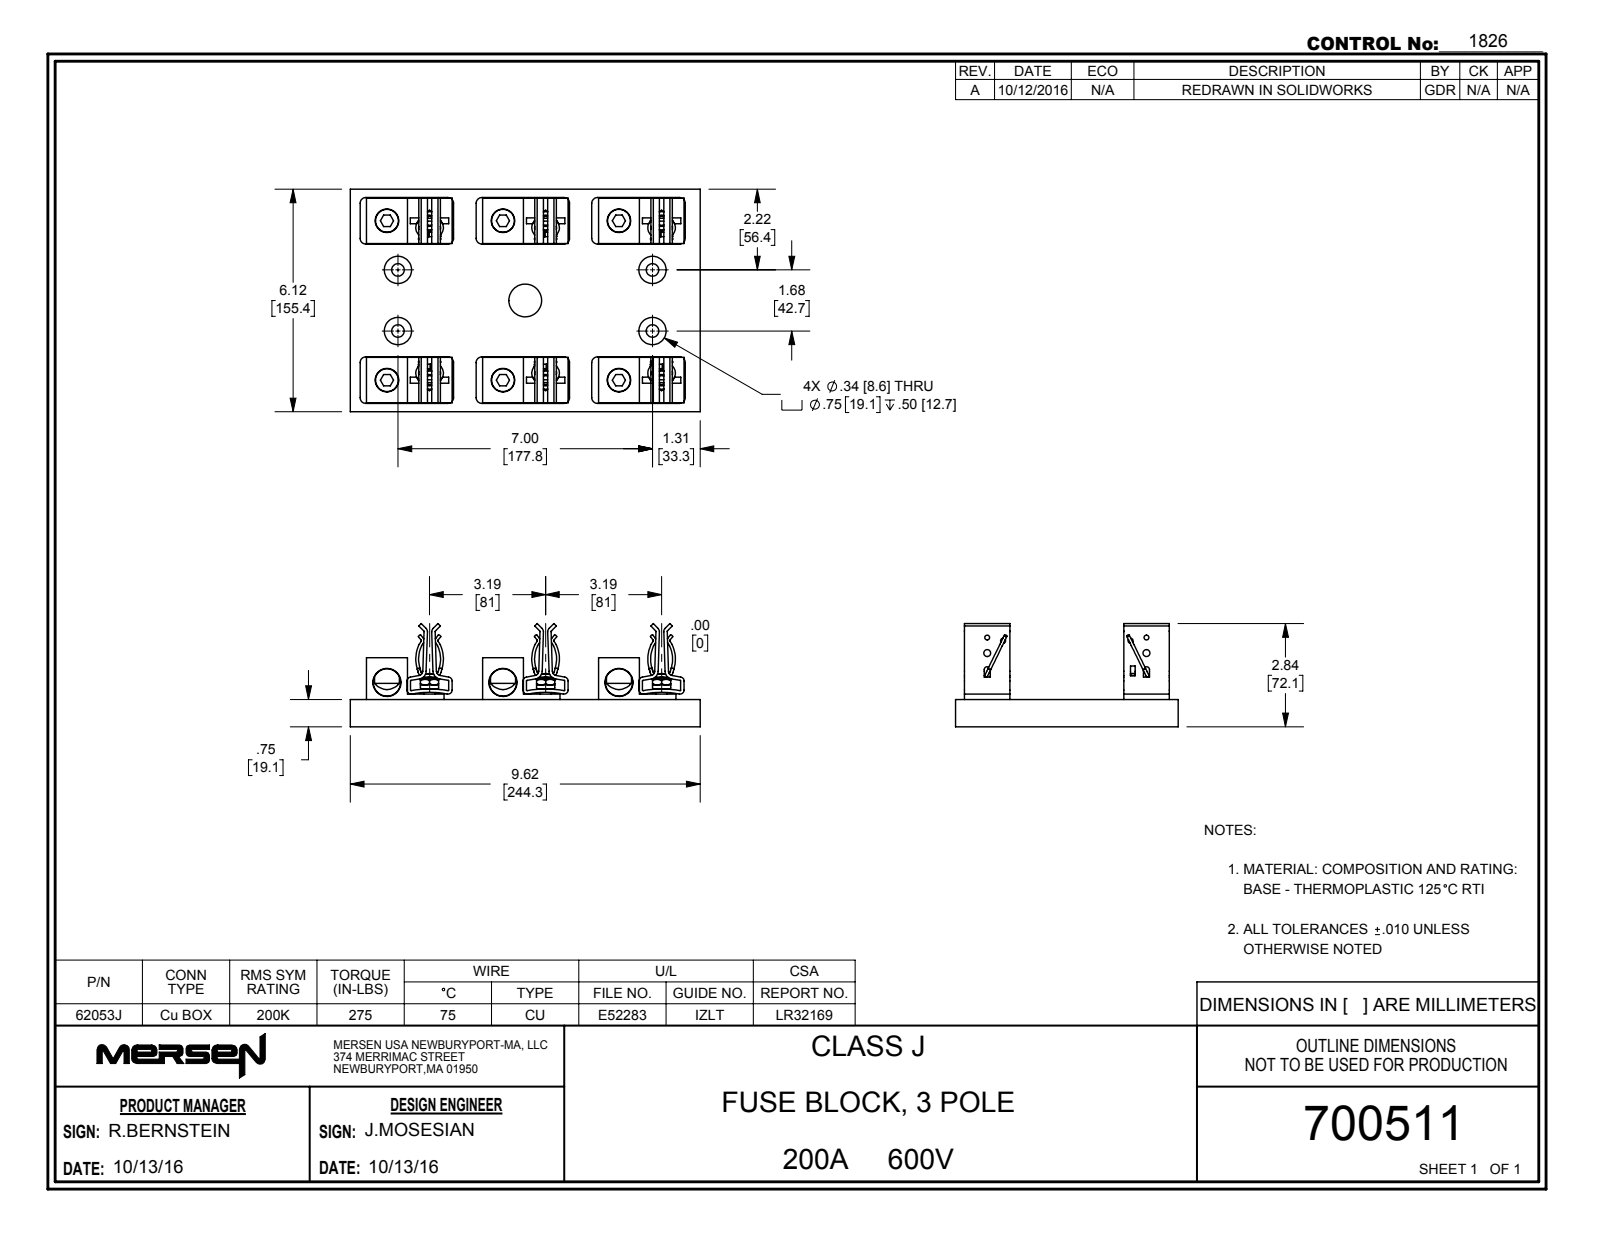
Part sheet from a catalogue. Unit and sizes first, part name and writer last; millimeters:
Units: millimetres
Overall size (bounding box): 244.3 × 155.4 × 72.1
Round holes (diameter × count): ⌀19.1 ×7, ⌀8 ×6, ⌀8.6 ×6, ⌀21.6 ×6, ⌀15.9 ×5, ⌀8.7 ×4, ⌀3.4 ×2, ⌀3.5 ×2, ⌀4.8 ×2, ⌀15.9 ×1
Round bosses / shafts (diameter × count): ⌀2 ×20, ⌀17.5 ×6, ⌀12.7 ×6, ⌀26.7 ×4, ⌀15.1 ×4
Partial cylindrical surfaces — rounded edges, fillets, slot ends (radius × count): R4.1 ×24, R7.2 ×18, R0.4 ×12, R1.7 ×12, R2.8 ×12, R3.2 ×12, R0.8 ×6, R4.4 ×6
Main face-to-face distances: 3.2, 2.5, 3.2, 0.6, 81, 31.8, 111.3, 2.5, 5.7, 97.5
Hole centre spacings: 111.3, 115.2, 81, 81, 162.1, 29.8, 51.3, 110.8
Volume: 503 900 mm³ · Surface area: 301 700 mm²
Bodies: 43 solids, 1513 faces (848 planar, 412 cylindrical, 253 other)
Part name (STEP PRODUCT): 700511revA
STEP written by: SolidWorks 2017 (AUTOMOTIVE_DESIGN)
